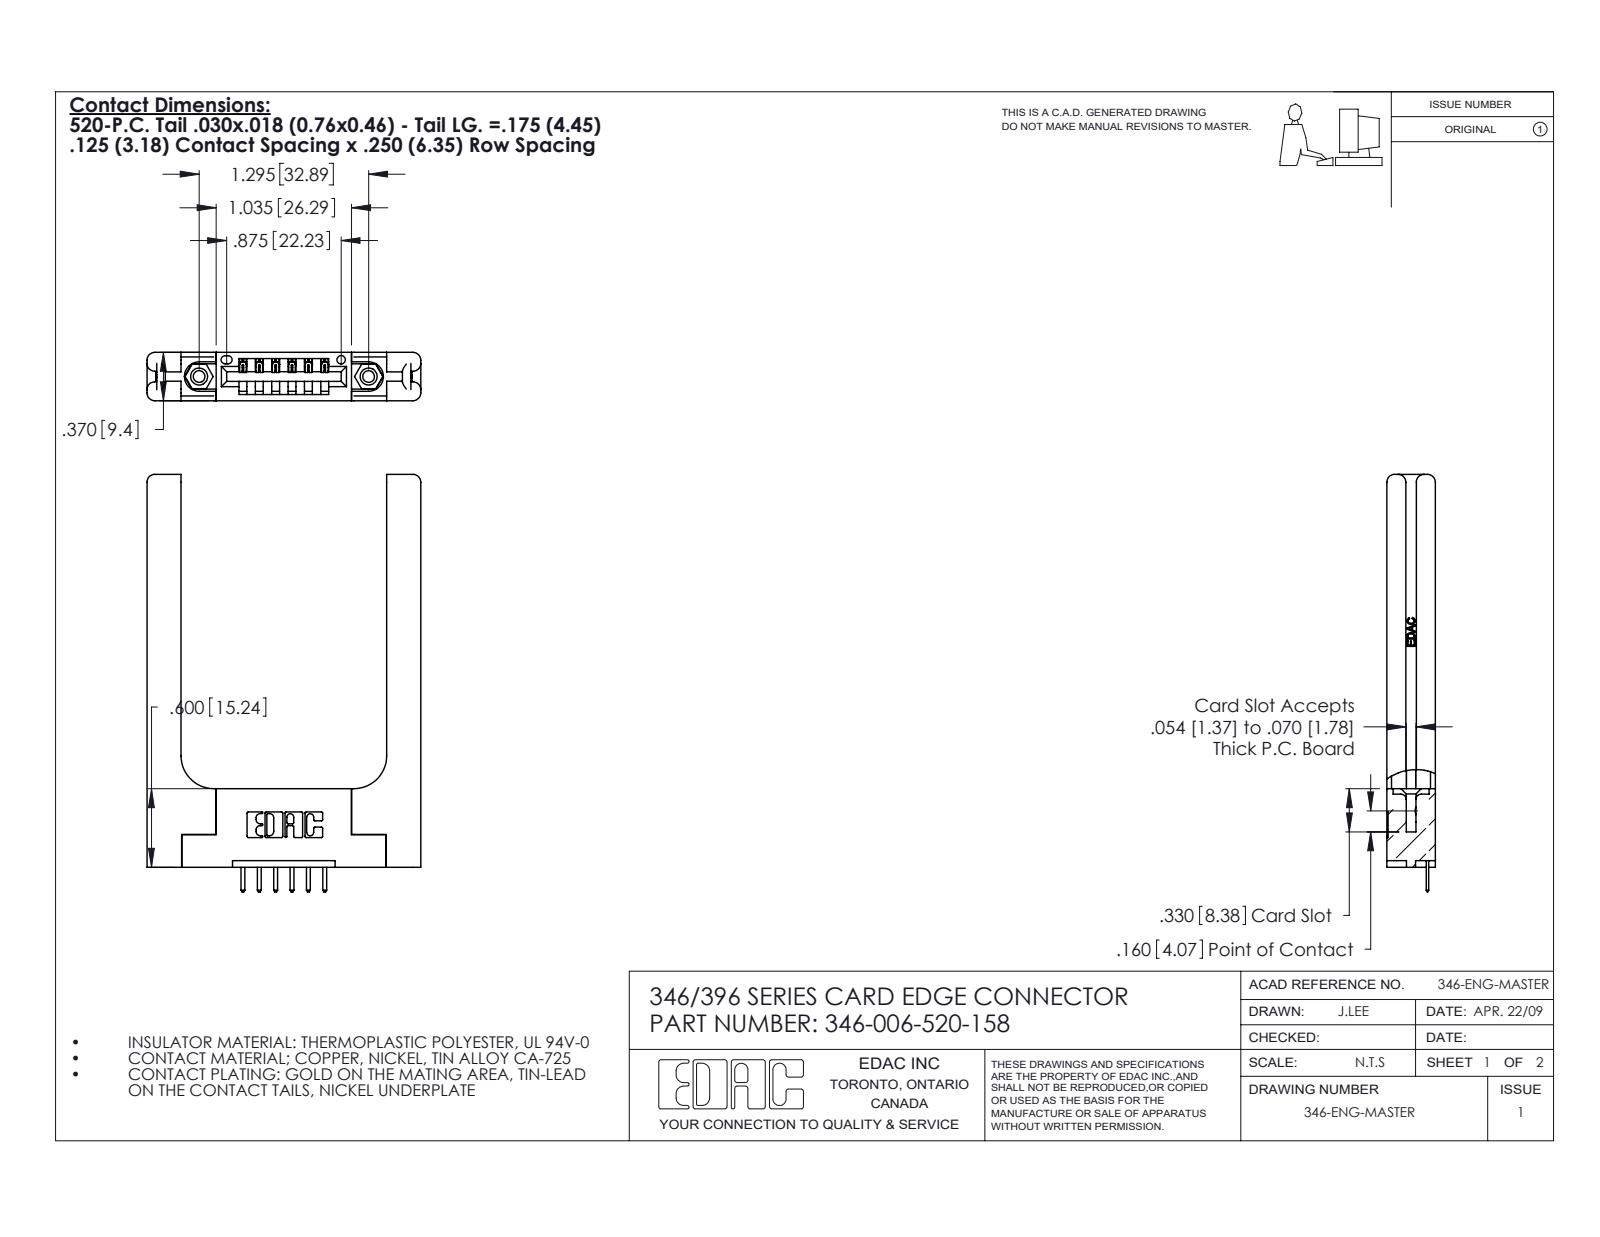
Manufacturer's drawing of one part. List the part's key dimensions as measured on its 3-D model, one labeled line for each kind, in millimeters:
Part name (STEP PRODUCT): 345-250-001_345-250-001-102; 345-292-001_345-293-120; 346-220-058_345-220-058; 346 Part_Flush Mounting Lugs - 0.156 Dia-TH (+1 more)
STEP written by: SolidWorks 2020 (CONFIG_CONTROL_DESIGN)
Units: millimetres
Bodies: 11 solids, 764 faces (490 planar, 214 cylindrical, 60 other)
Overall size (bounding box): 81 × 53.1 × 9.4
Volume: 12 300 mm³ · Surface area: 10 750 mm²
Round holes (diameter × count): ⌀2.3 ×2, ⌀3.2 ×2, ⌀4 ×2, ⌀1.6 ×1
Round bosses / shafts (diameter × count): ⌀3.9 ×2
Partial cylindrical surfaces — rounded edges, fillets, slot ends (radius × count): R0.3 ×22, R1.5 ×16, R0.3 ×14, R0.2 ×12, R0.2 ×6, R0.8 ×6, R0.7 ×3, R0.8 ×2
Main face-to-face distances: 9.4, 3.8, 5.6, 6.4, 1.8, 39.9, 3.8, 1.8, 1.2, 8.2
Hole centre spacings: 6.2, 27.7, 32.9
